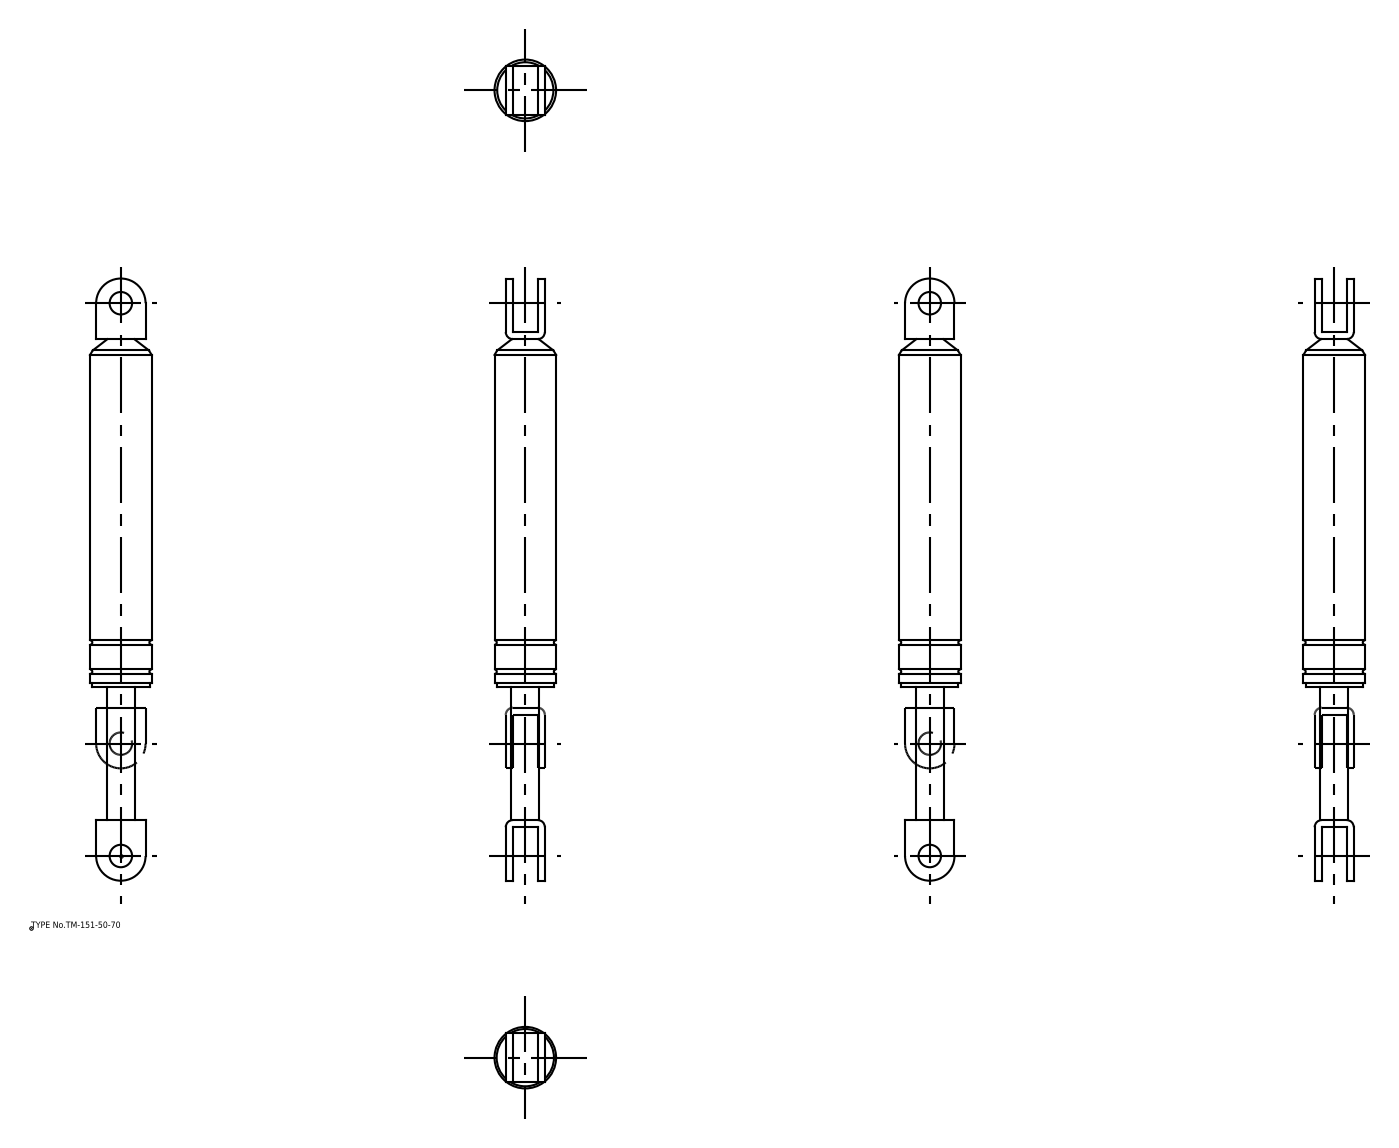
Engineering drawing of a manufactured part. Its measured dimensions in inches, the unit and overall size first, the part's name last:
Units: inches
Overall size (bounding box): 10.551 × 1.11 × 1.11
Round holes (diameter × count): ⌀0.394 ×2
Round bosses / shafts (diameter × count): ⌀1.11 ×1, ⌀1.079 ×1, ⌀1.004 ×1, ⌀0.492 ×1
Partial cylindrical surfaces — rounded edges, fillets, slot ends (radius × count): R0.126 ×4, R0.433 ×2
Main face-to-face distances: 0.126, 0.559, 0.685, 0.433, 0.866, 8.551, 2.449, 8.677, 6.228, 6.102
Hole centre spacings: 9.685
Volume: 6.366 in³ · Surface area: 34.78 in²
Bodies: 2 solids, 64 faces (22 planar, 32 cylindrical, 10 other)
Part name (STEP PRODUCT): TM_151_50_70; TM_151_50_70_div
STEP written by: spGate 16.7.1 (AUTOMOTIVE_DESIGN)
